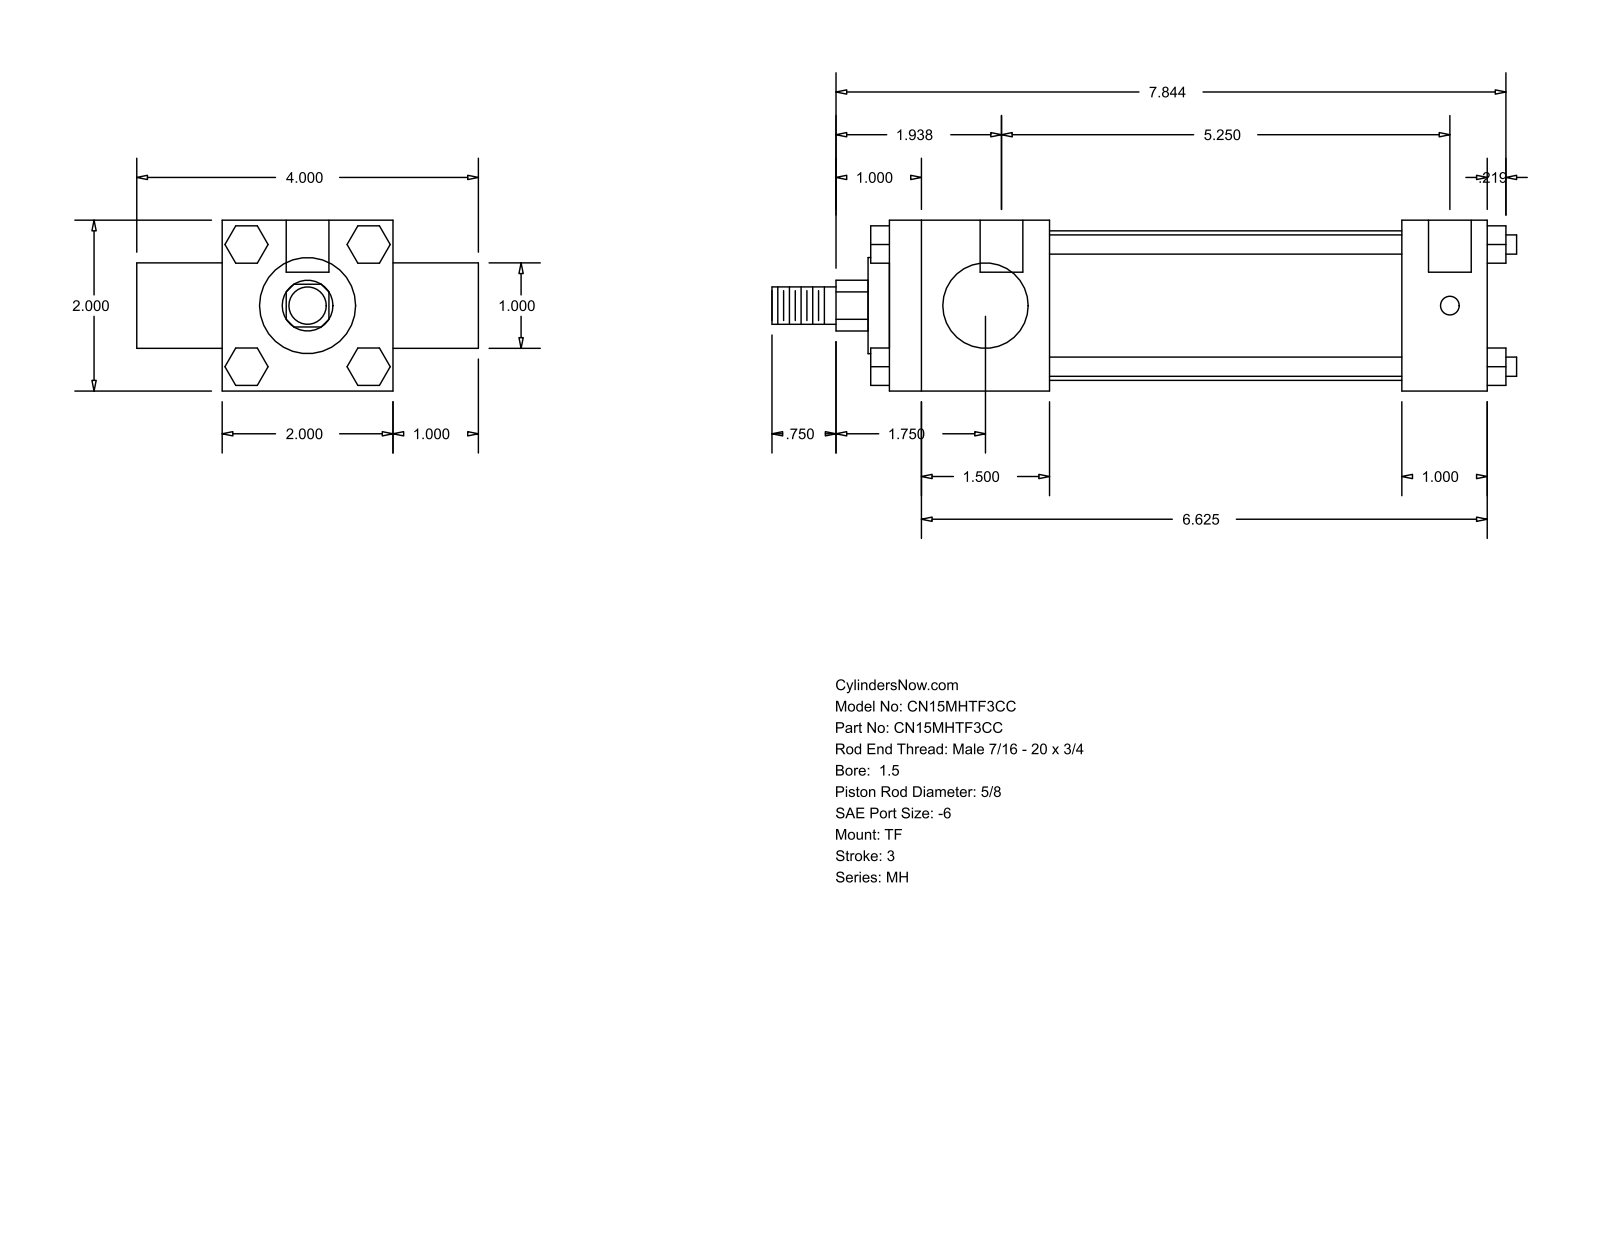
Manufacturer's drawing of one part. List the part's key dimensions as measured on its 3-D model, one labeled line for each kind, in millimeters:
Part name (STEP PRODUCT): MH_TF__0150_0.625
STEP written by: GSSL Pune (CONFIG_CONTROL_DESIGN)
Units: millimetres
Bodies: 0 solids, 120 faces (92 planar, 28 cylindrical, 0 other)
Overall size (bounding box): 221.46 × 101.6 × 50.8
Round holes (diameter × count): ⌀5.56 ×3, ⌀12.7 ×2
Round bosses / shafts (diameter × count): ⌀5.71 ×4, ⌀44.45 ×1, ⌀28.57 ×1, ⌀25.4 ×1, ⌀15.88 ×1, ⌀11.11 ×1
Partial cylindrical surfaces — rounded edges, fillets, slot ends (radius × count): R7.54 ×1
Main face-to-face distances: 50.8, 25.4, 177.8, 76.2, 47.62, 130.18, 152.4, 104.78, 11.11, 18.16
Hole centre spacings: 3.17, 133.35, 136.52
